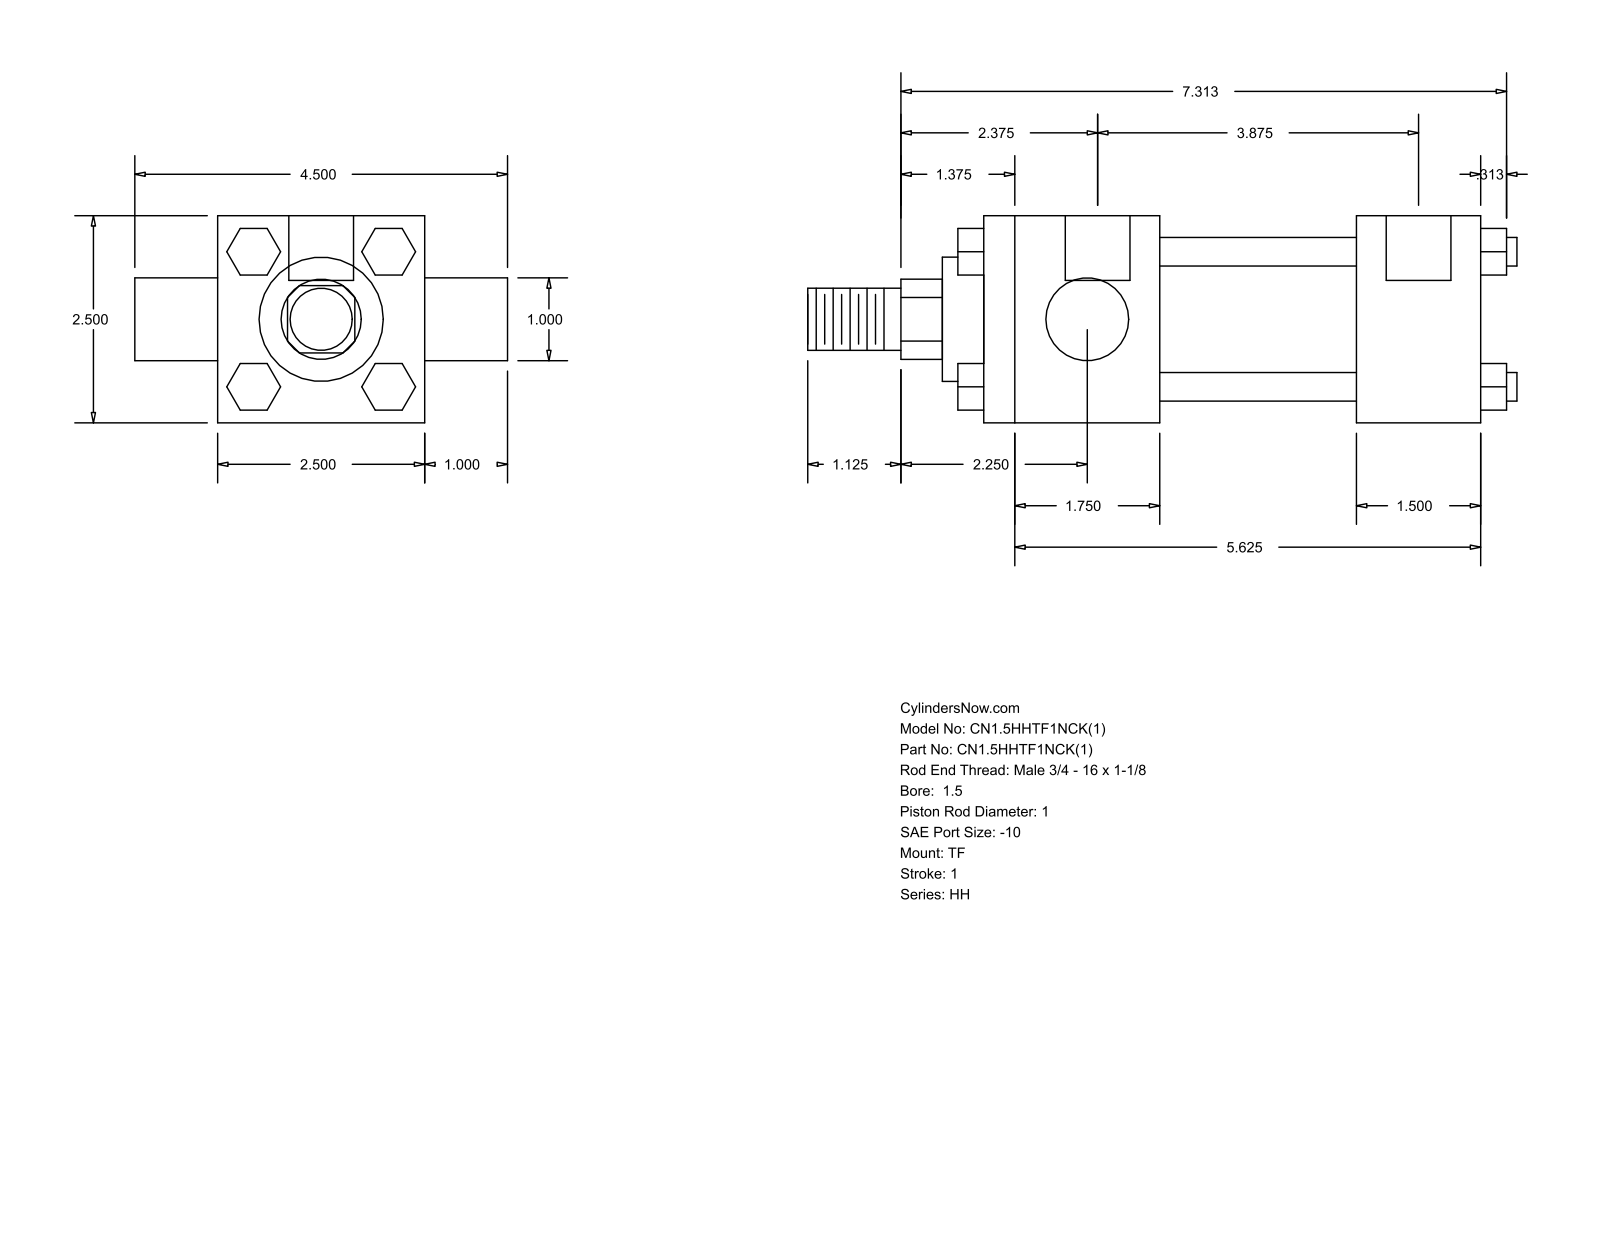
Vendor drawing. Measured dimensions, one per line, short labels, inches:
name: HH_TF__0150_1
written by: GSSL Pune (CONFIG_CONTROL_DESIGN)
unit: in
bodies: 0 solids, 120 faces (92 planar, 28 cylindrical, 0 other)
size: 8.563 × 4.5 × 2.5
holes: 3× ⌀0.219, 2× ⌀0.781
bosses: 4× ⌀0.345, 2× ⌀1, 1× ⌀1.75, 1× ⌀1.5, 1× ⌀0.75
rounds: 1× R0.484
face distances: 2.5, 4.5, 1.5, 3.875, 2.375, 2.125, 6, 1, 0.815, 0.563
hole spacings: 0.063, 3.937, 3.875, 4
